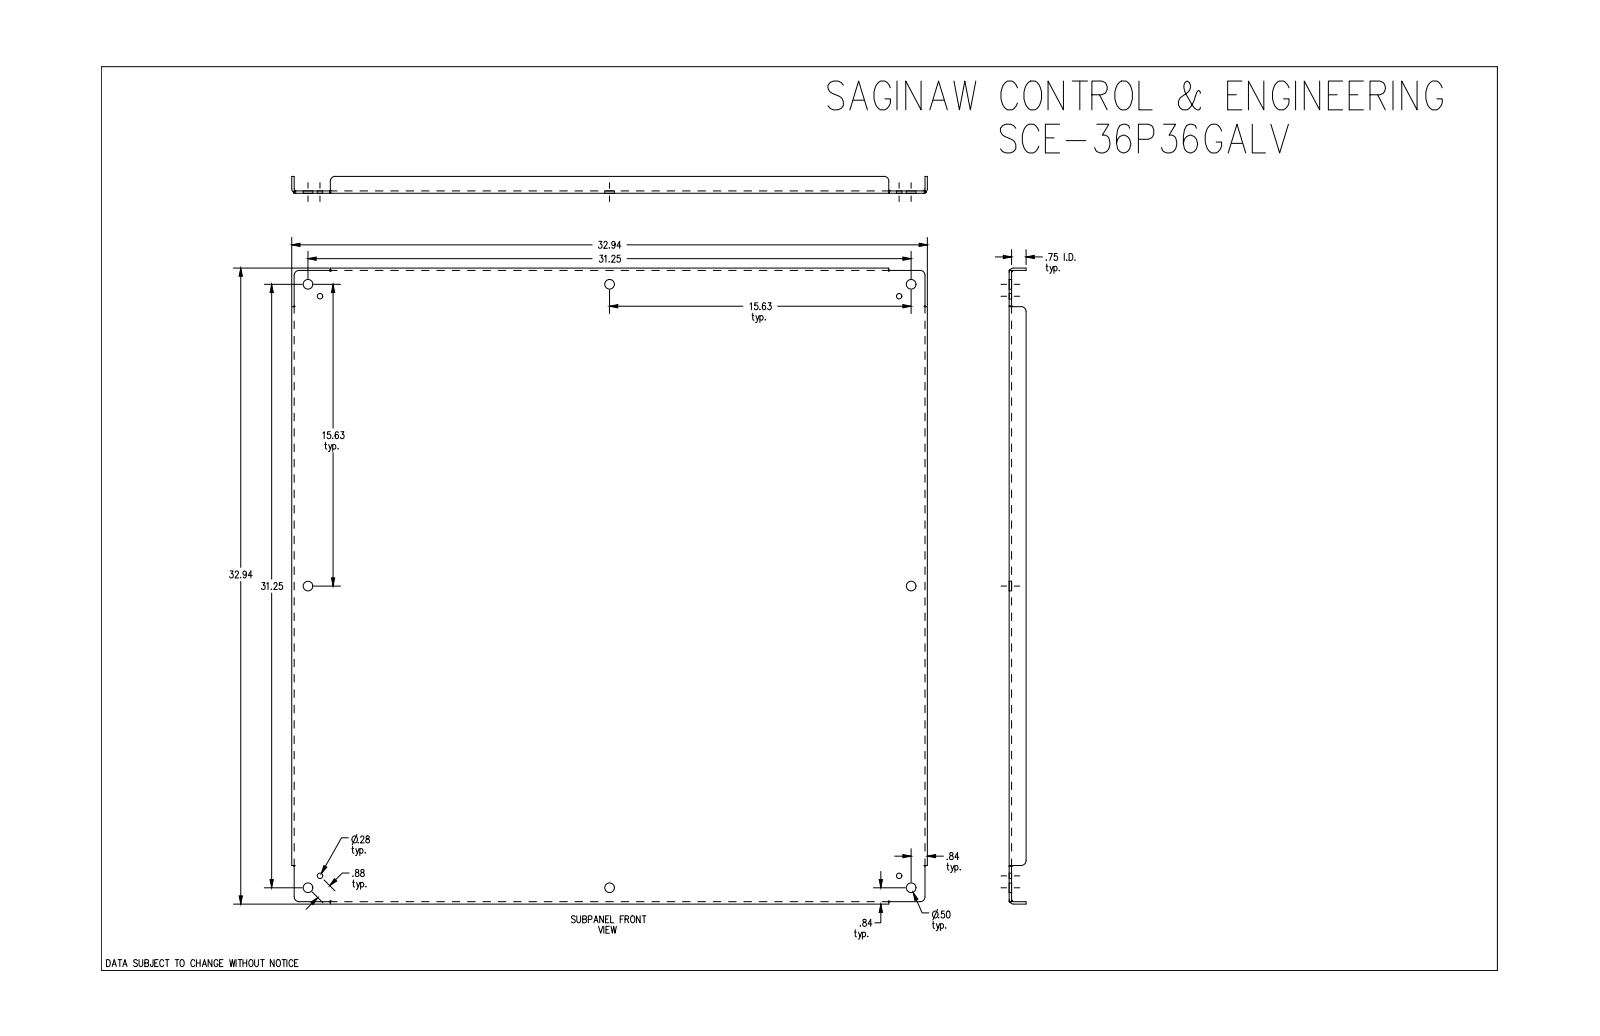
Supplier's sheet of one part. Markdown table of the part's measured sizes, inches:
| quantity | value |
| --- | --- |
| part name | SCE-36P36GALV |
| STEP written by | SolidWorks 2019 (CONFIG_CONTROL_DESIGN) |
| units | inches |
| bodies | 1 solid, 86 faces (30 planar, 32 cylindrical, 24 other) |
| overall size | 32.938 × 32.938 × 0.875 |
| volume | 144.9 in³ |
| surface area | 2 337 in² |
| round holes (diameter × count) | 0.5 × 8, 0.281 × 4 |
| partial cylindrical surfaces (radius × count) | 0.25 × 8, 0.112 × 4, 0.237 × 4 |
| main face-to-face distances | 0.125, 0.125, 32.813, 32.687, 32.938, 0.75, 0.875, 2, 30.938, 1.875 |
| hole center spacings | 15.019, 15.625, 30.638, 34.11, 34.939, 31.25, 0.875, 22.097 |
